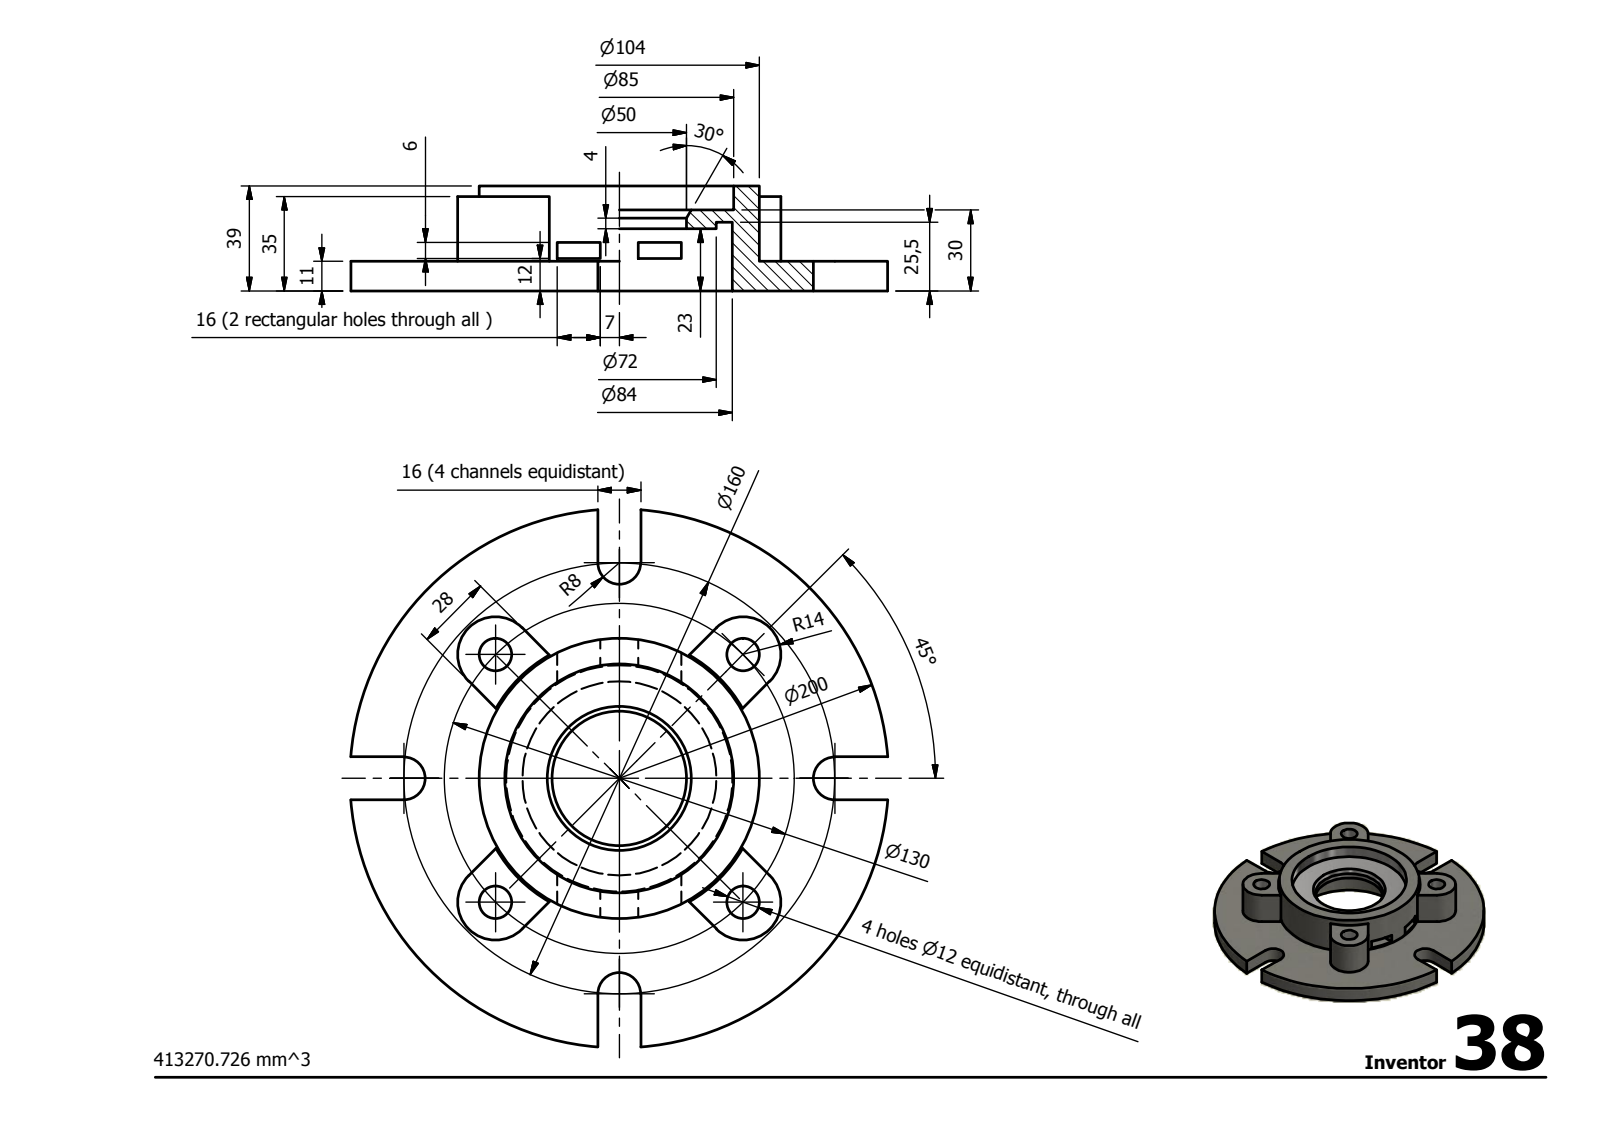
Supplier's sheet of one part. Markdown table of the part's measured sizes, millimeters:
| quantity | value |
| --- | --- |
| STEP written by | Autodesk Inventor 2014 (AUTOMOTIVE_DESIGN) |
| units | millimeters |
| bodies | 1 solid, 68 faces (42 planar, 25 cylindrical, 1 other) |
| overall size | 199.36 × 199.36 × 39 |
| volume | 413 271 mm³ |
| surface area | 99 477 mm² |
| round holes (diameter × count) | 12 × 4, 50 × 1, 84 × 1, 85 × 1 |
| round bosses / shafts (diameter × count) | 200 × 1, 104 × 1, 72 × 1 |
| partial cylindrical surfaces (radius × count) | 8 × 4, 14 × 4, 52.61 × 1 |
| main face-to-face distances | 11, 12, 28, 30, 19, 16, 5, 39, 9, 23 |
| hole center spacings | 65, 91.92, 129.99 |
